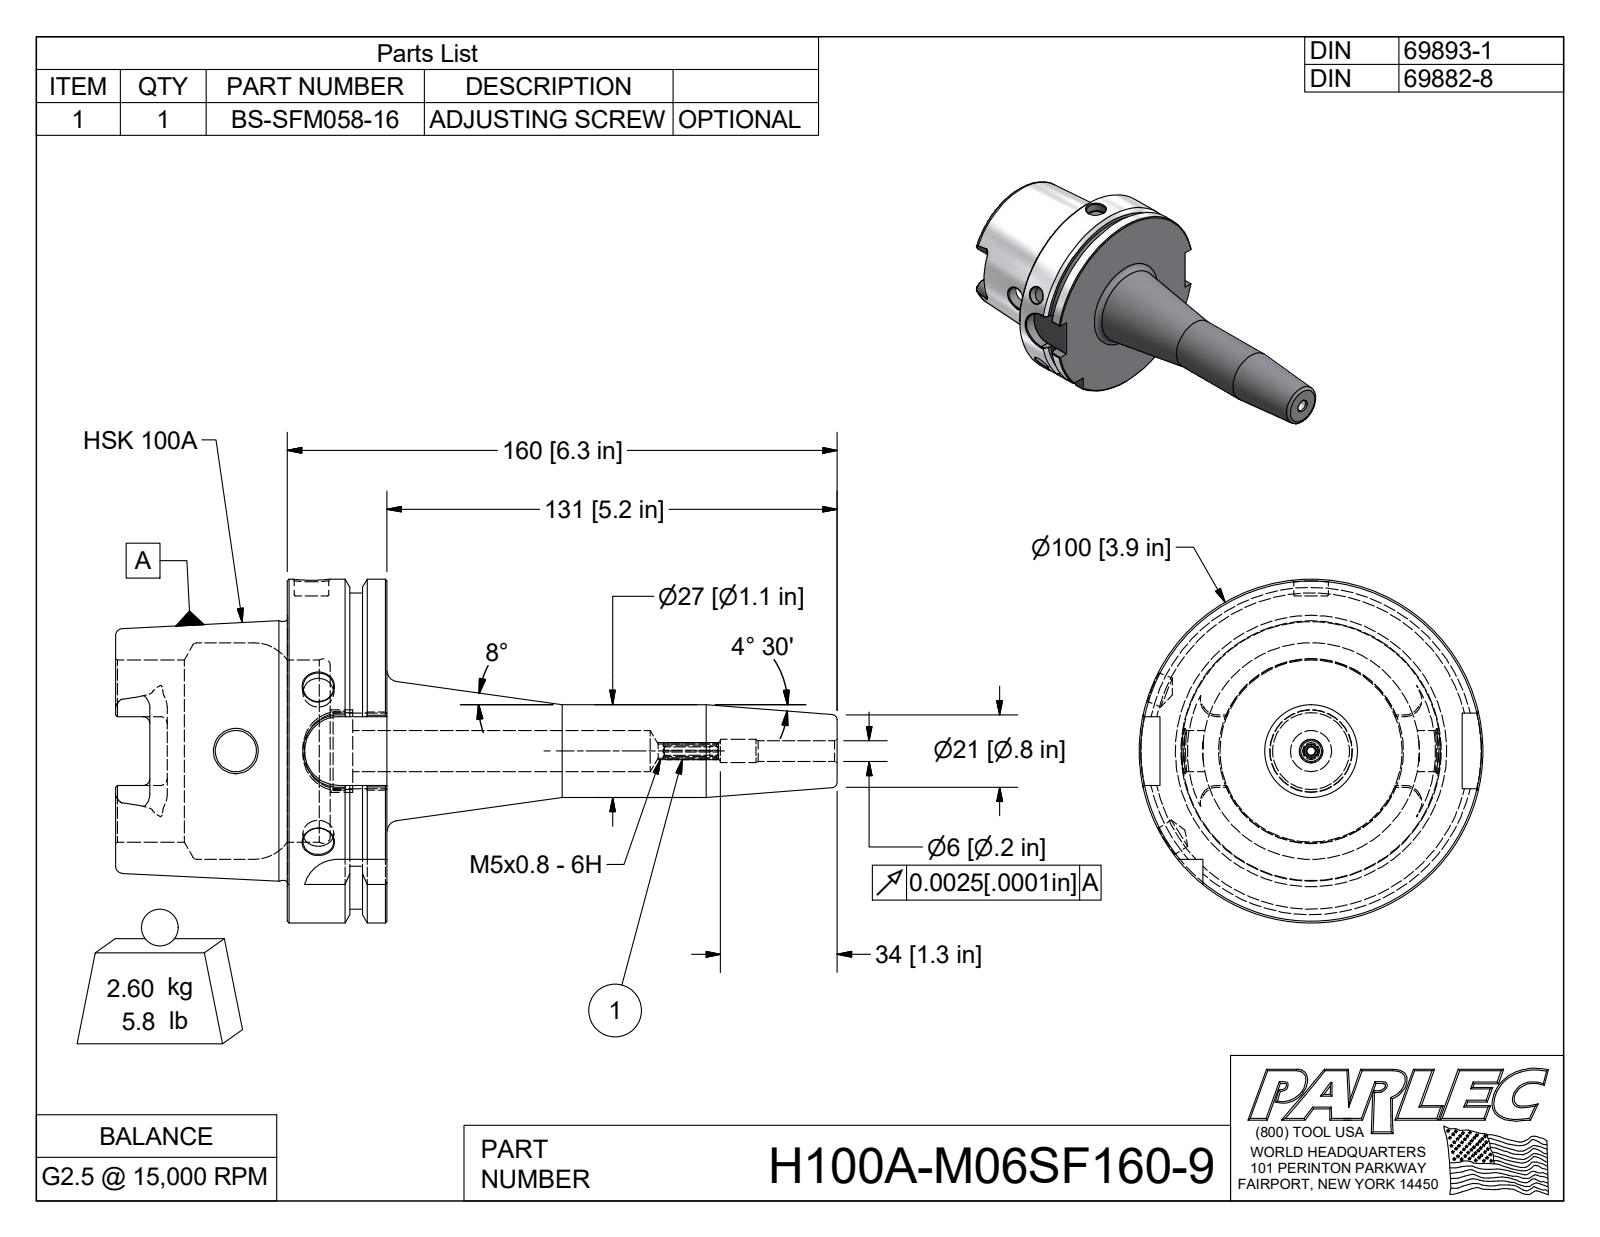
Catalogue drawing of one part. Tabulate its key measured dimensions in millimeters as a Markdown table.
| quantity | value |
| --- | --- |
| part name | H100A-M06SF160-9; H100A-M06SF160-9-1; BS-SFM058-16 |
| STEP written by | Autodesk Inventor 2009 (AUTOMOTIVE_DESIGN) |
| units | millimeters |
| bodies | 2 solids, 148 faces (48 planar, 29 cylindrical, 71 other) |
| overall size | 210 × 100 × 100 |
| volume | 335 800 mm³ |
| surface area | 64 520 mm² |
| round holes (diameter × count) | 6 × 1, 6.8 × 1, 10 × 1, 12 × 1, 22.4 × 1, 53 × 1, 63 × 1 |
| round bosses / shafts (diameter × count) | 100 × 1, 75.4 × 1, 27 × 1 |
| partial cylindrical surfaces (radius × count) | 10 × 4, 2 × 3, 4.9 × 2, 2.5 × 1, 46 × 1 |
| main face-to-face distances | 29, 12.5, 16.5, 50, 62.5, 79, 68.1, 18.1, 5.6, 10.9 |
